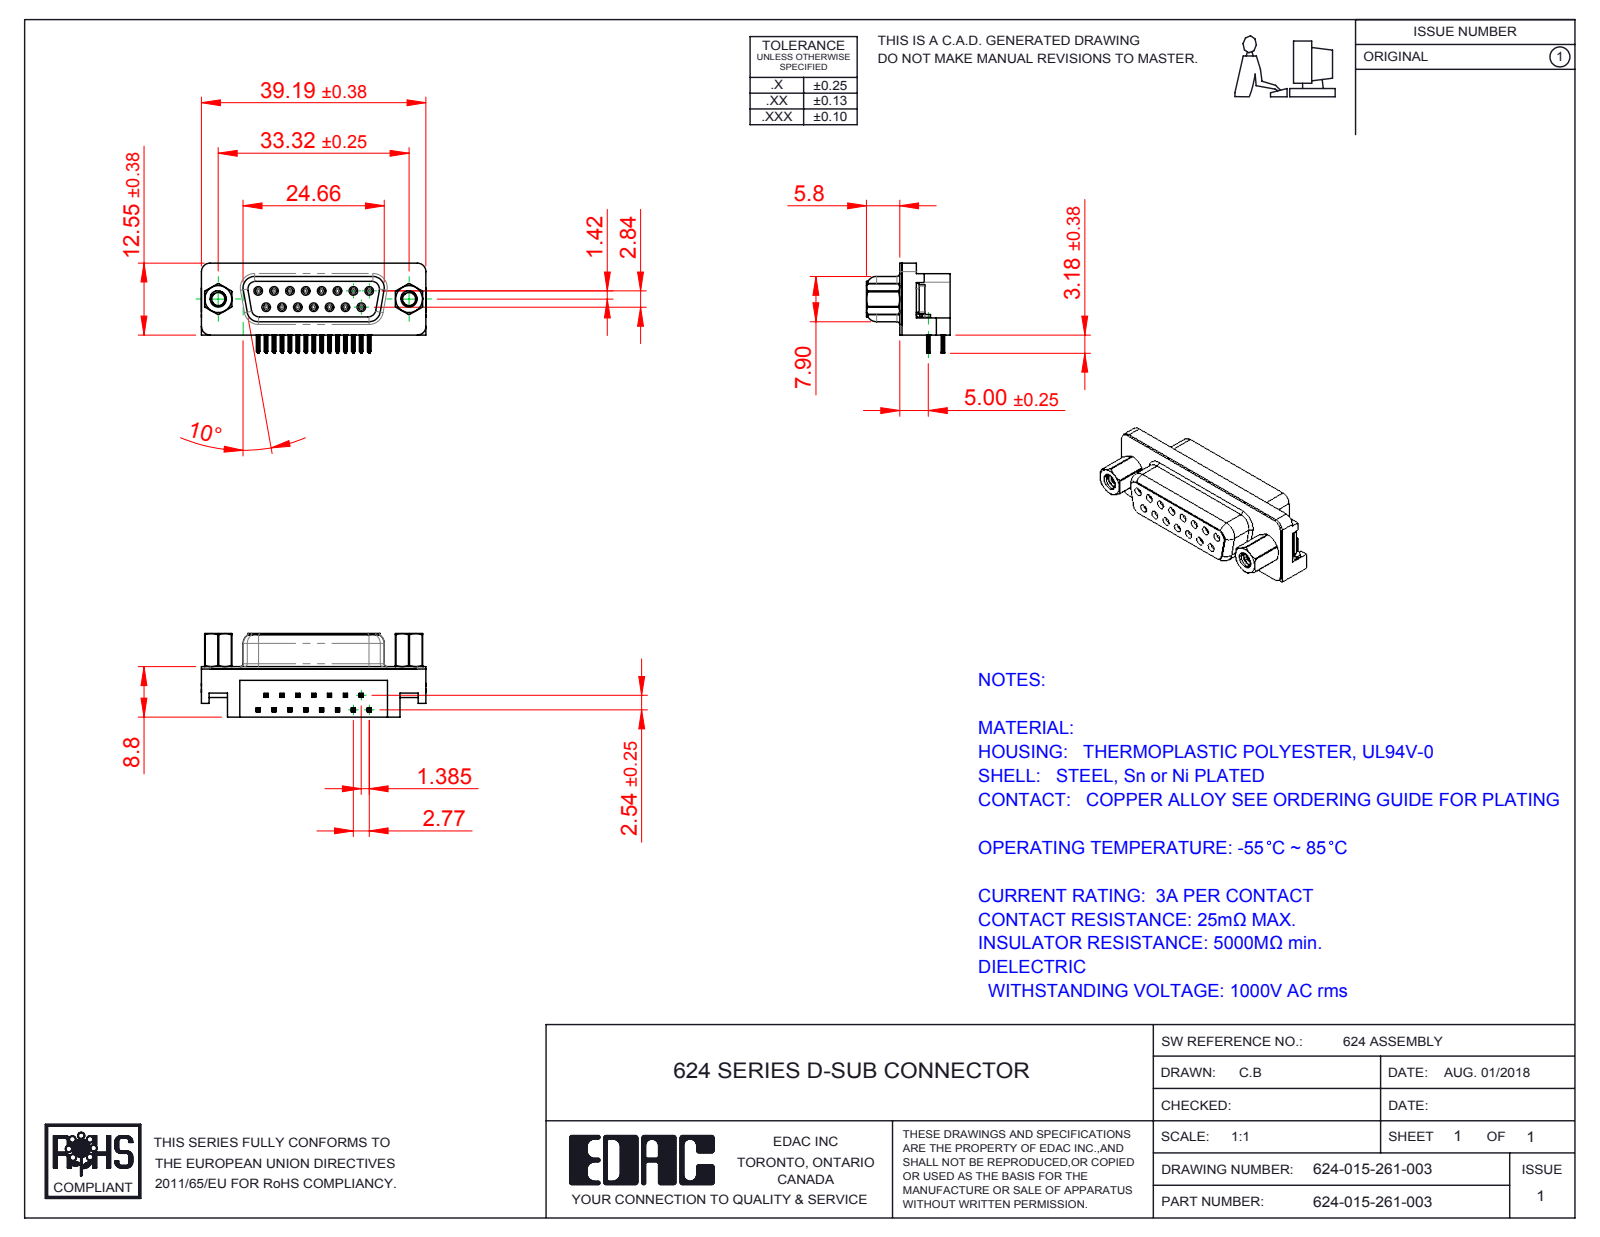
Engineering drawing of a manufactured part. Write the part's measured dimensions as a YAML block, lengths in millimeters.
part_name: "624 Contact Top; 624 Non Board Mount; 624-015-261-003; 624 Shell_15 Socket (+4 more)"
step_written_by: "SolidWorks 2016 (CONFIG_CONTROL_DESIGN)"
units: millimeters
bodies: {solids: 23, faces: 2469, planar: 1024, cylindrical: 663, other: 782}
overall_size: [39.22, 15.73, 14.6]
volume: 4283
surface_area: 6265
round_holes:
  - {diameter: 0.8, count: 15}
  - {diameter: 0.9, count: 15}
  - {diameter: 2.26, count: 2}
  - {diameter: 2.29, count: 2}
  - {diameter: 4, count: 2}
  - {diameter: 4.8, count: 2}
  - {diameter: 5, count: 2}
round_bosses_or_shafts:
  - {diameter: 1.2, count: 15}
  - {diameter: 4.9, count: 2}
  - {diameter: 4.75, count: 2}
  - {diameter: 3.9, count: 2}
  - {diameter: 2.79, count: 2}
partial_cylinders:
  - {radius: 0.1, count: 120}
  - {radius: 0.15, count: 60}
  - {radius: 0.35, count: 30}
  - {radius: 1, count: 18}
  - {radius: 0.34, count: 15}
  - {radius: 0.25, count: 8}
  - {radius: 1.35, count: 8}
  - {radius: 1.5, count: 8}
face_to_face_distances: [0.4, 6.2, 8.4, 8.8, 9.38, 3.18, 2.9, 5.9, 2.5, 2.73]
hole_center_spacings: [3.16, 2.77, 5.54, 8.31, 11.08, 5.03, 5.04, 7.48]
